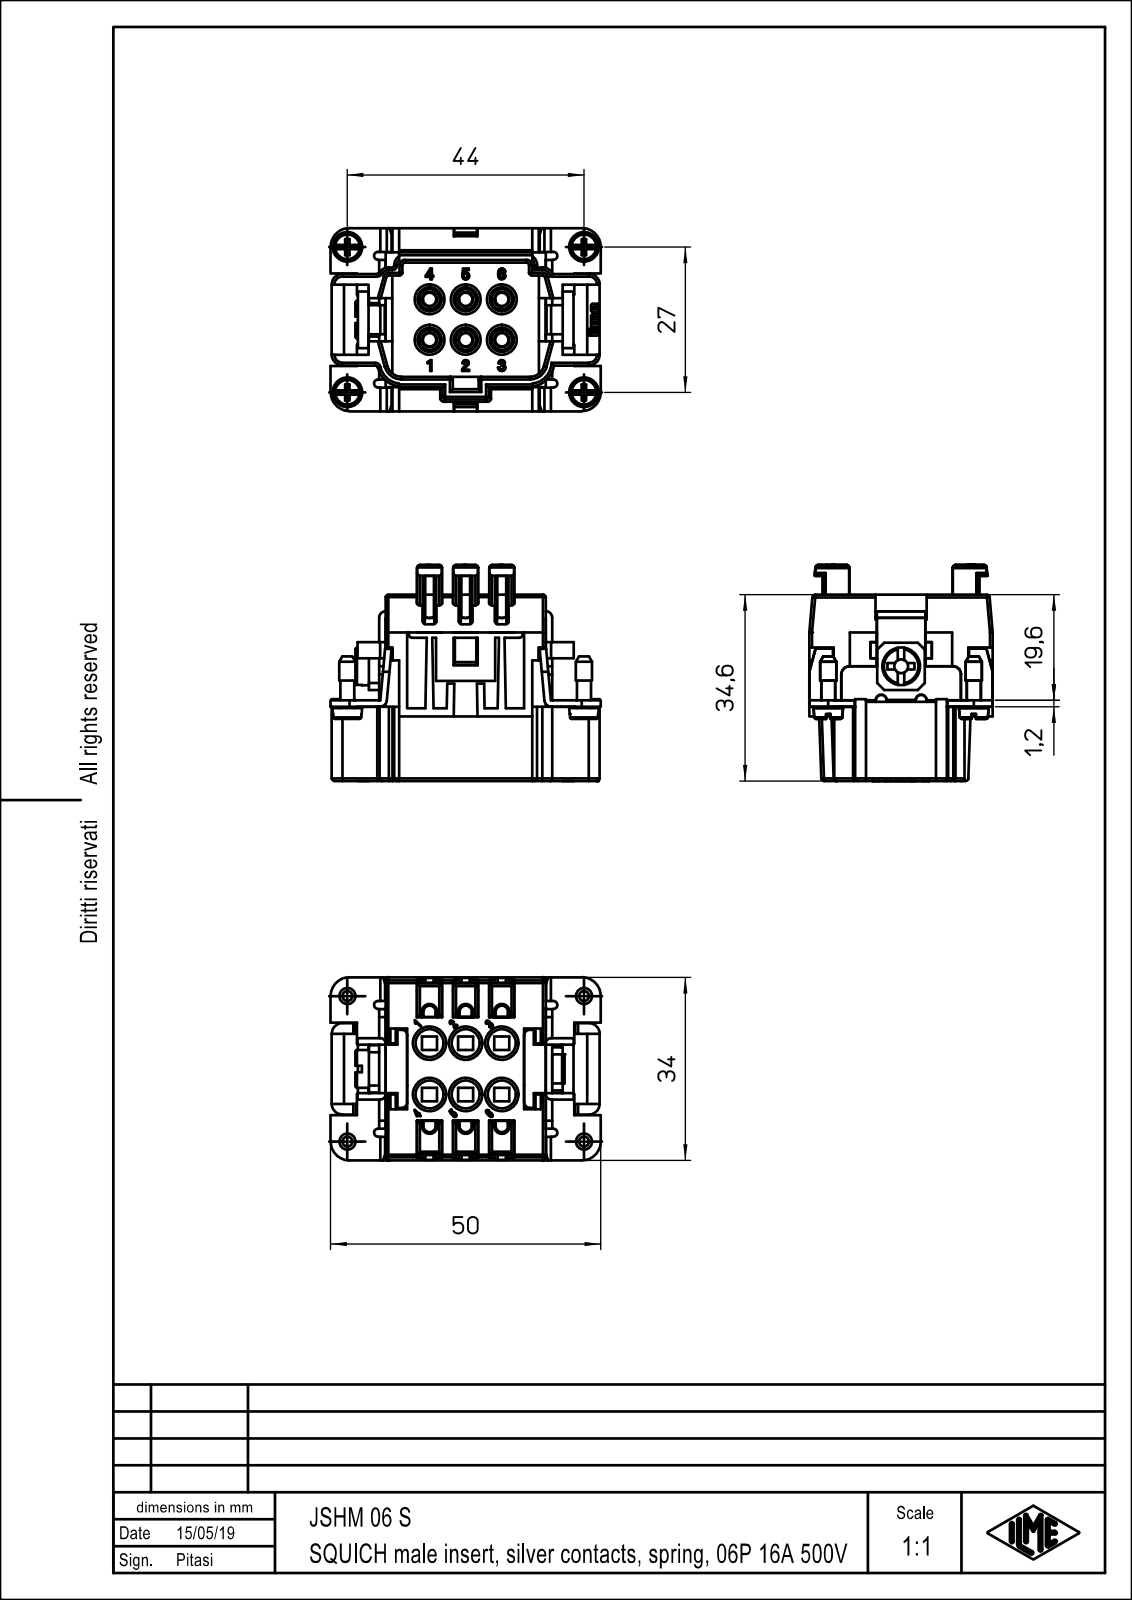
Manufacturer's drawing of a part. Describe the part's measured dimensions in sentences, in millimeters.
The part is named "JSHM_06_S". Its 3-D file was written by "Creo Elements/Direct Modeling 20.1B 02-Apr-2019 (C) Parametric Technology GmbH (AUTOMOTIVE_DESIGN)". It is 1 solid with 1179 faces: 733 planar, 313 cylindrical and 133 other. Overall it measures 50.1 by 40.1 by 34 millimeters. Its volume is 24 256 cubic millimeters and its surface area 18 261 square millimeters. Round holes: 6 of diameter 5.2, 4 of diameter 2.8, 1 of diameter 2.58, 1 of diameter 4.2. Round bosses or shafts: 6 of diameter 2.48, 4 of diameter 5.5, 4 of diameter 3, 4 of diameter 2.6, 1 of diameter 7, 1 of diameter 6, 1 of diameter 4. Partial cylindrical surfaces (rounded edges, fillets, slot ends): 91 of radius 0.5, 15 of radius 0.3, 12 of radius 1, 10 of radius 2, 6 of radius 1.15, 6 of radius 1.2, 4 of radius 0.75, 4 of radius 3.5. The main face-to-face distances are 1.5, 12.5, 4, 1.2, 14, 7, 27.6, 1, 2, 2.1. The hole center spacings are 6.7, 11.62, 17.58, 23.63, 23.78, 28.55, 29.96, 33.97.
